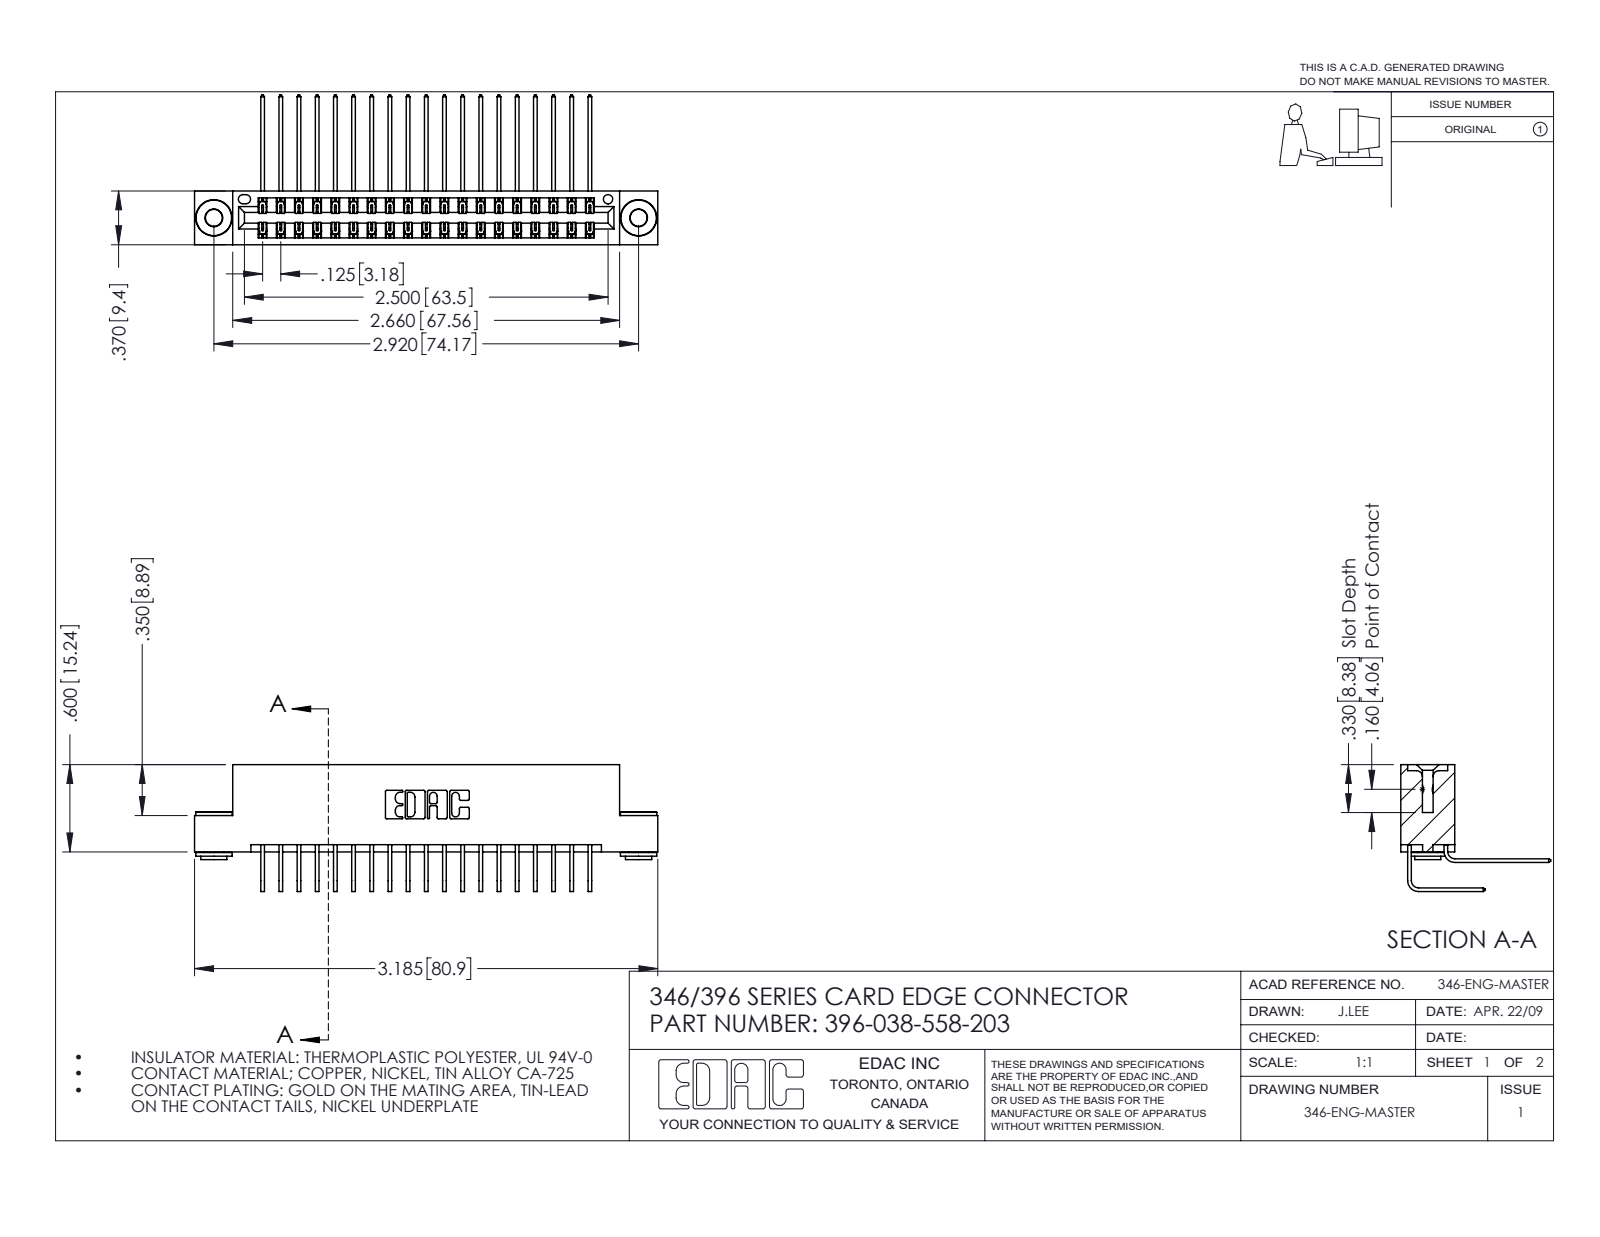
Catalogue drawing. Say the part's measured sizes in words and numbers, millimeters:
The part is named "345-292-001_558 Tail - 2; 346 Part_Flush Mounting Lugs - 0.156 Dia-TH; 345-250-002_345-250-002-102; 396-038-558-203 (+1 more)". Its 3-D file was written by "SolidWorks 2016 (CONFIG_CONTROL_DESIGN)". It is 41 solids with 2212 faces: 1492 planar, 712 cylindrical and 8 other. Overall it measures 80.9 by 26.2 by 22.2 millimeters. Its volume is 7 950 cubic millimeters and its surface area 11 830 square millimeters. Round holes: 2 of diameter 2.9, 2 of diameter 4, 1 of diameter 1.6. Round bosses or shafts: 2 of diameter 6.4, 2 of diameter 4.6, 2 of diameter 3.5. Partial cylindrical surfaces (rounded edges, fillets, slot ends): 57 of radius 0.2, 22 of radius 0.3, 6 of radius 0.2, 6 of radius 0.8, 3 of radius 0.7, 2 of radius 0.4, 2 of radius 0.6, 2 of radius 0.6. The main face-to-face distances are 8.2, 1.2, 6.4, 0.6, 9.4, 7.6, 1.8, 7, 3.8, 5.6. The hole center spacings are 6.2, 68.9, 74.2.
